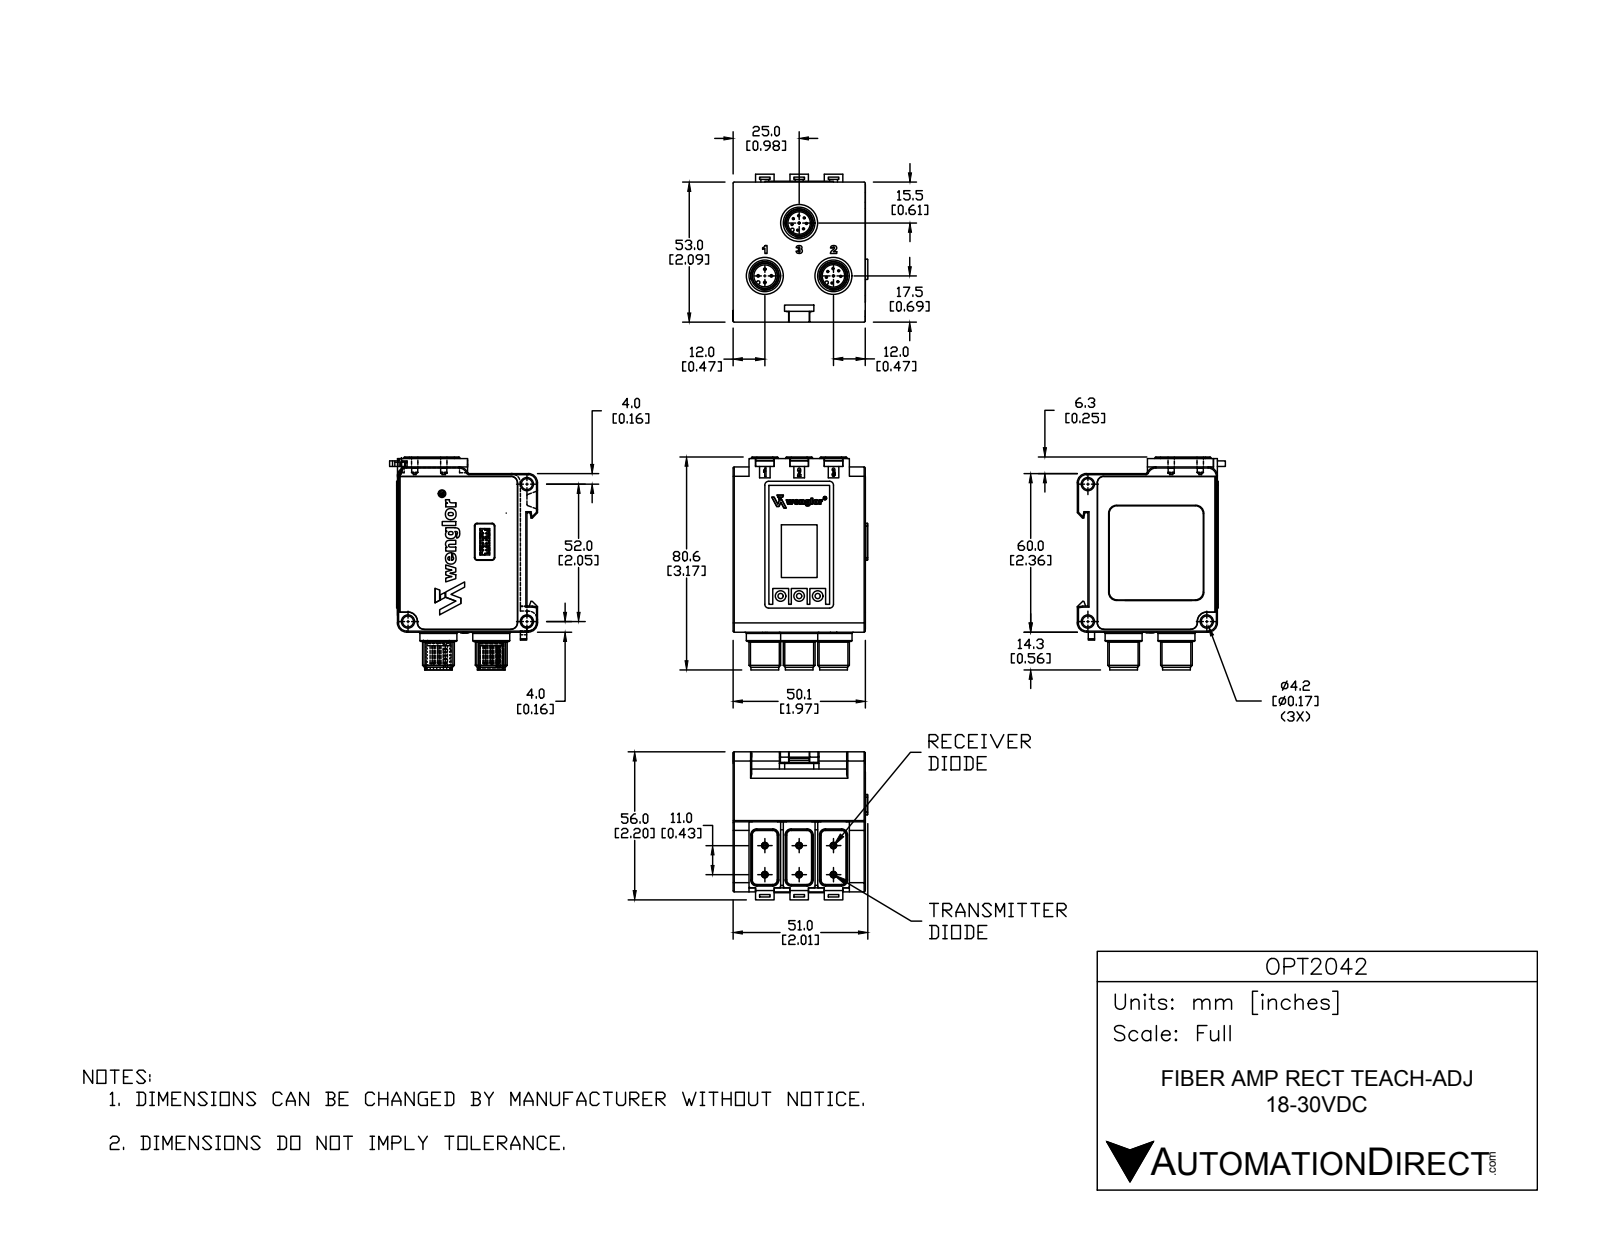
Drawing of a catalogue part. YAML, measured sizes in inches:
part_name: "OPT2042"
step_written_by: "SolidWorks 2014 (AUTOMOTIVE_DESIGN)"
units: inches
bodies: {solids: 1, faces: 1407, planar: 663, cylindrical: 441, other: 303}
overall_size: [3.173, 2.205, 2.006]
volume: 9.383
surface_area: 42.73
round_holes:
  - {diameter: 0.071, count: 6}
  - {diameter: 0.091, count: 6}
  - {diameter: 0.094, count: 6}
  - {diameter: 0.039, count: 3}
  - {diameter: 0.047, count: 3}
  - {diameter: 0.157, count: 3}
  - {diameter: 0.165, count: 3}
  - {diameter: 0.376, count: 3}
  - {diameter: 0.335, count: 2}
  - {diameter: 0.138, count: 1}
  - {diameter: 0.173, count: 1}
  - {diameter: 0.327, count: 1}
round_bosses_or_shafts:
  - {diameter: 0.031, count: 16}
  - {diameter: 0.02, count: 12}
  - {diameter: 0.039, count: 4}
  - {diameter: 0.551, count: 3}
  - {diameter: 0.472, count: 3}
  - {diameter: 0.413, count: 3}
  - {diameter: 0.37, count: 3}
  - {diameter: 0.315, count: 3}
partial_cylinders:
  - {radius: 0.016, count: 61}
  - {radius: 0.008, count: 29}
  - {radius: 0.012, count: 16}
  - {radius: 0.118, count: 12}
  - {radius: 0.03, count: 9}
  - {radius: 0.006, count: 8}
  - {radius: 0.138, count: 8}
  - {radius: 0.004, count: 7}
face_to_face_distances: [1.97, 1.831, 1.967, 1.843, 0.013, 0.098, 2.362, 1.929, 1.942, 0.248]
hole_center_spacings: [0.512, 1.024, 0.67, 0.433, 1.111, 0.518, 0.622, 0.67]
